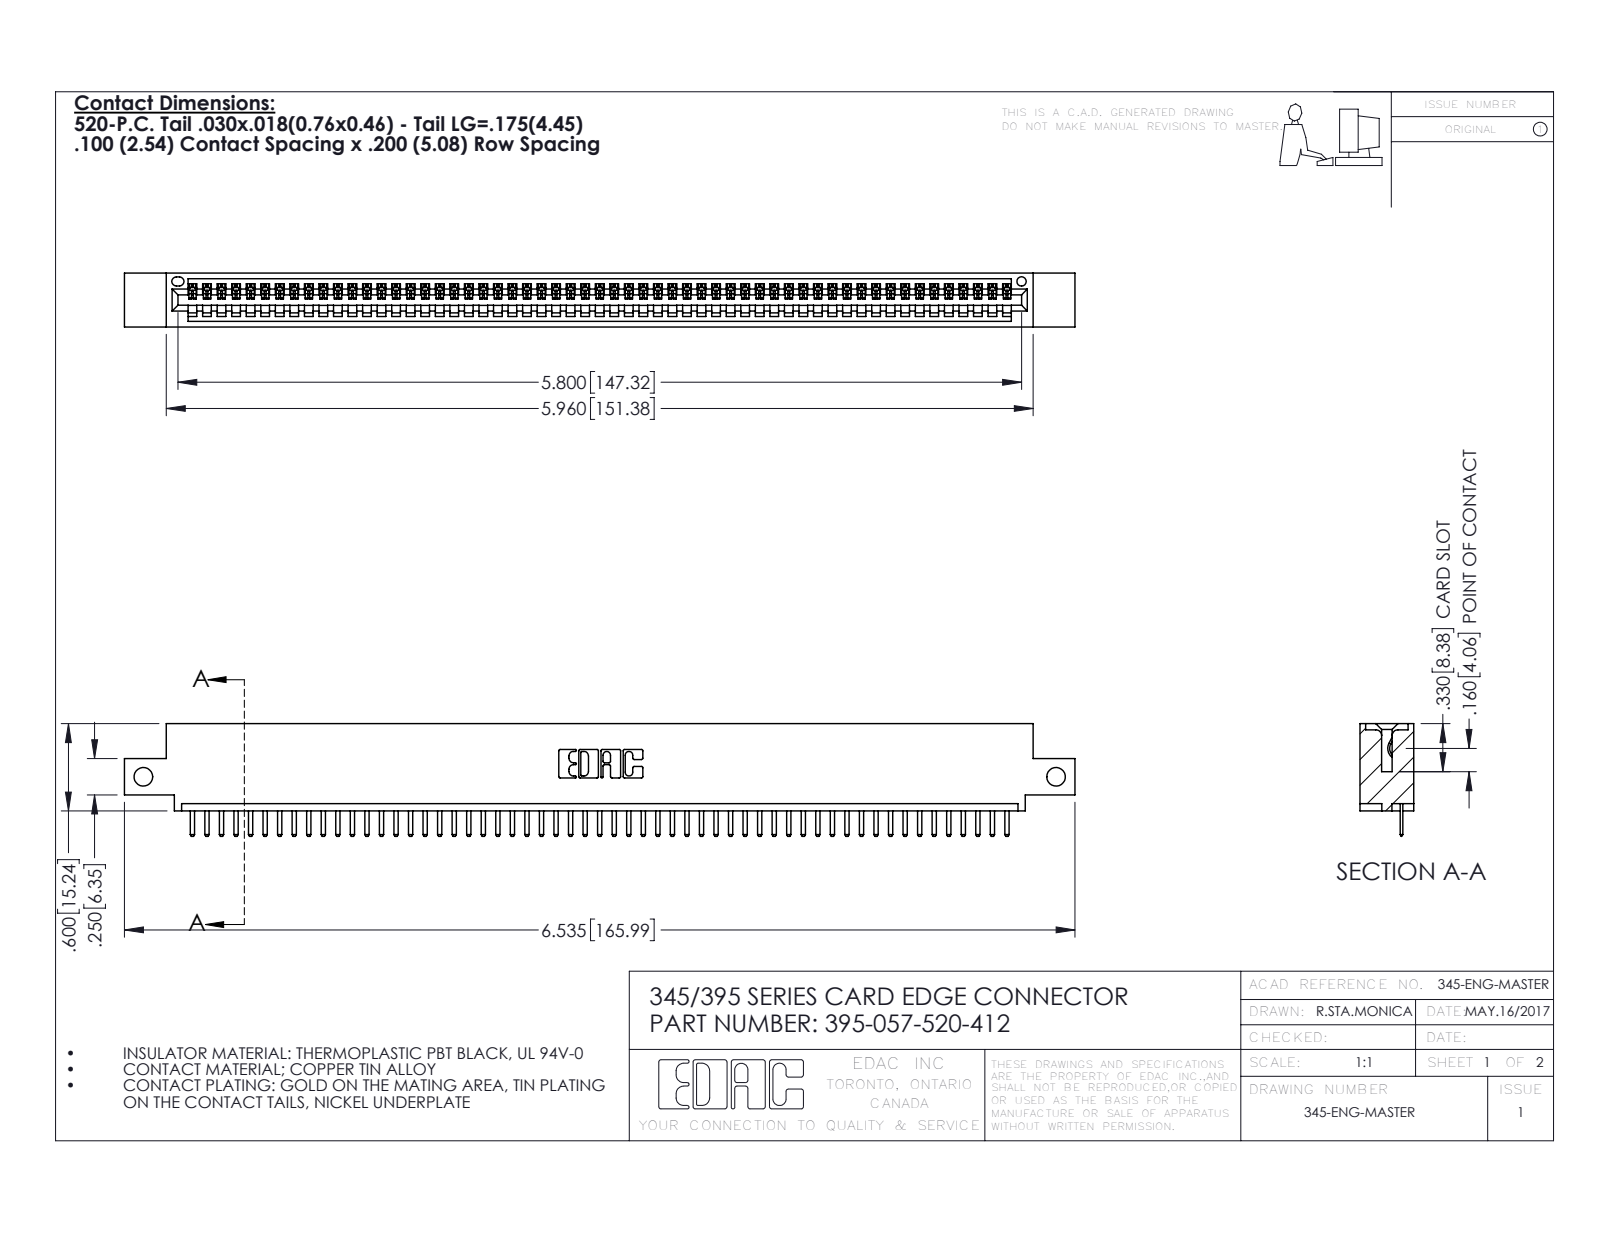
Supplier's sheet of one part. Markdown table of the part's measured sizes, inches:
| quantity | value |
| --- | --- |
| part name | 345-292-001_345-293-120; 395-057-520-412; 345 Part_0.110 Offset - Side Mount |
| STEP written by | SolidWorks 2016 (CONFIG_CONTROL_DESIGN) |
| units | inches |
| bodies | 58 solids, 3664 faces (2478 planar, 1186 cylindrical, 0 other) |
| overall size | 6.535 × 0.775 × 0.37 |
| volume | 0.95 in³ |
| surface area | 31.45 in² |
| round holes (diameter × count) | 0.128 × 2, 0.064 × 1 |
| partial cylindrical surfaces (radius × count) | 0.01 × 116, 0.006 × 114, 0.01 × 22, 0.007 × 6, 0.031 × 6, 0.026 × 3, 0.031 × 2, 0.04 × 2 |
| main face-to-face distances | 0.298, 0.072, 0.37, 0.2, 0.098, 0.272, 0.025, 0.225, 0.072, 0.149 |
| hole center spacings | 6.275 |
